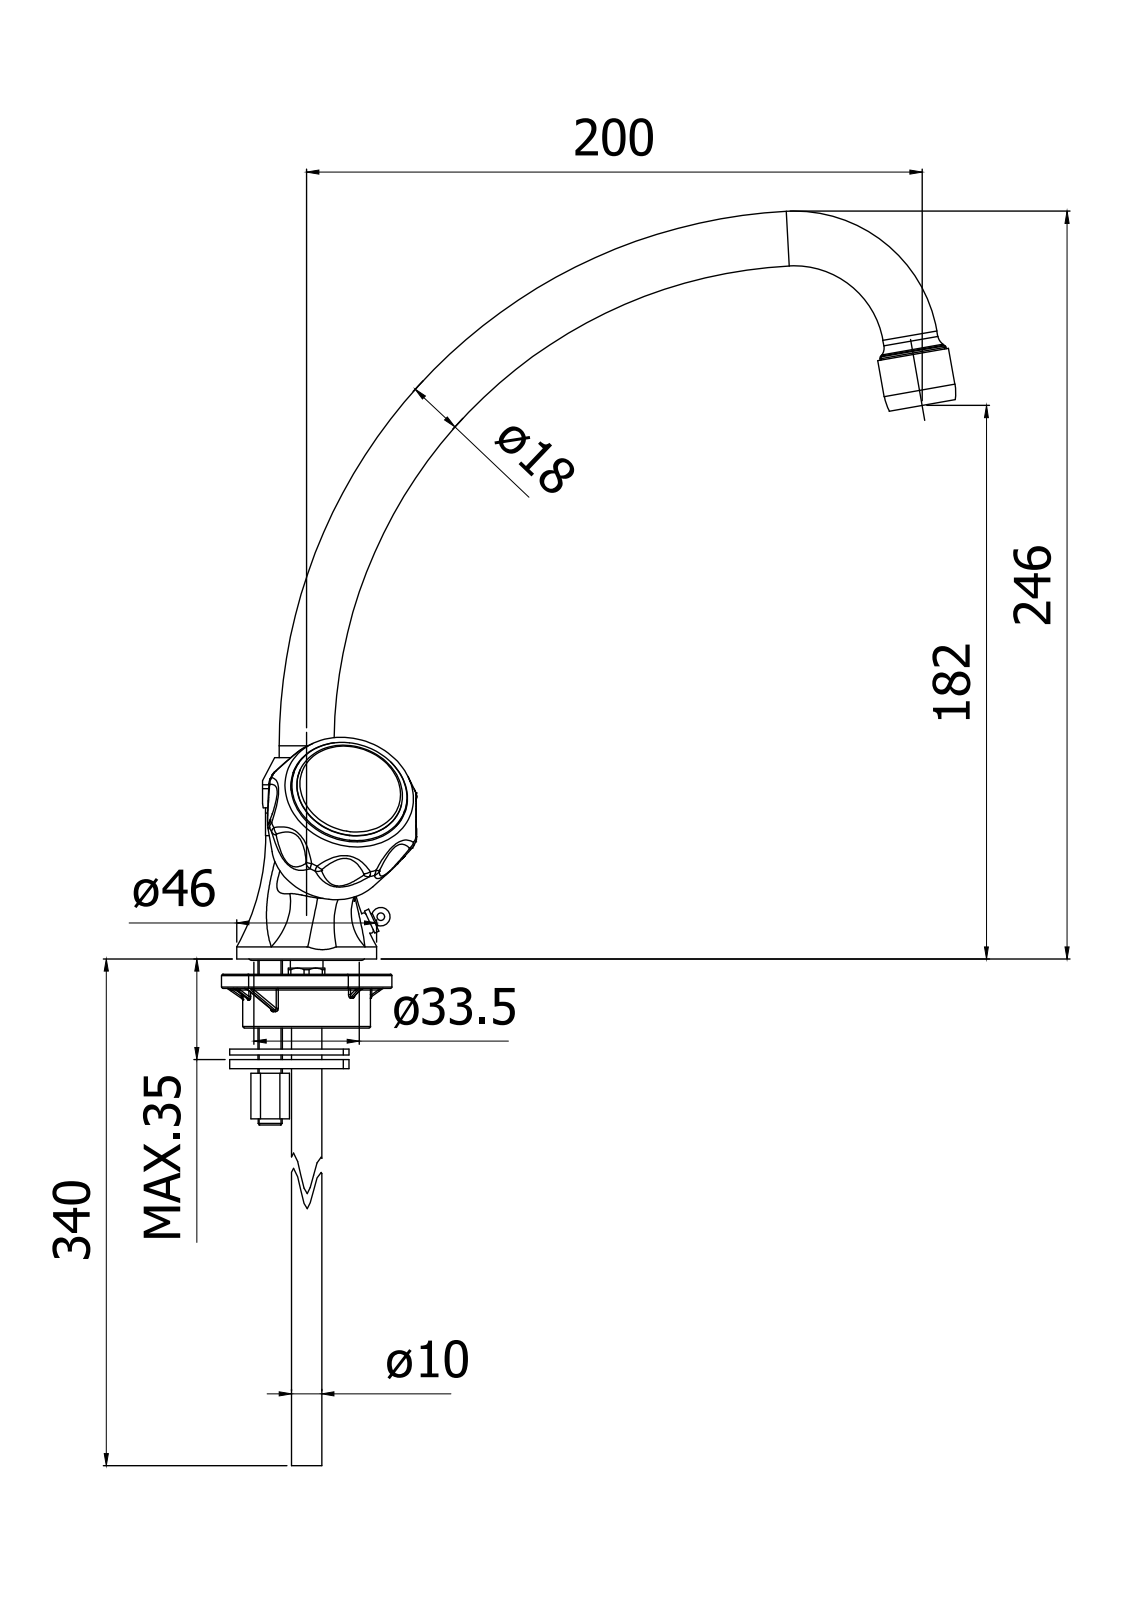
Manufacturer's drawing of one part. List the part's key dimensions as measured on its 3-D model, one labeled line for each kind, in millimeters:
Part name (STEP PRODUCT): DA078CR
STEP written by: CREO PARAMETRIC BY PTC INC, 2020044 (CONFIG_CONTROL_DESIGN)
Units: millimetres
Bodies: 1 solid, 375 faces (40 planar, 102 cylindrical, 233 other)
Overall size (bounding box): 245.9 × 236.31 × 145.89
Volume: 262 859 mm³ · Surface area: 59 312 mm²
Round holes (diameter × count): ⌀9 ×4, ⌀11 ×2, ⌀18 ×2, ⌀19 ×2, ⌀21.5 ×2, ⌀22 ×2, ⌀6 ×1, ⌀6.8 ×1, ⌀12 ×1, ⌀16.3 ×1, ⌀16.4 ×1, ⌀18.1 ×1
Round bosses / shafts (diameter × count): ⌀38.5 ×2, ⌀26 ×2, ⌀18 ×2, ⌀46 ×1, ⌀34 ×1, ⌀27 ×1, ⌀24 ×1, ⌀23.6 ×1
Partial cylindrical surfaces — rounded edges, fillets, slot ends (radius × count): R21.31 ×16, R18.5 ×1
Main face-to-face distances: 35.3, 0.4, 35.7, 56, 55.6, 20.3, 1.3, 66.16, 64.86, 55
Hole centre spacings: 7, 13.89, 12, 14
